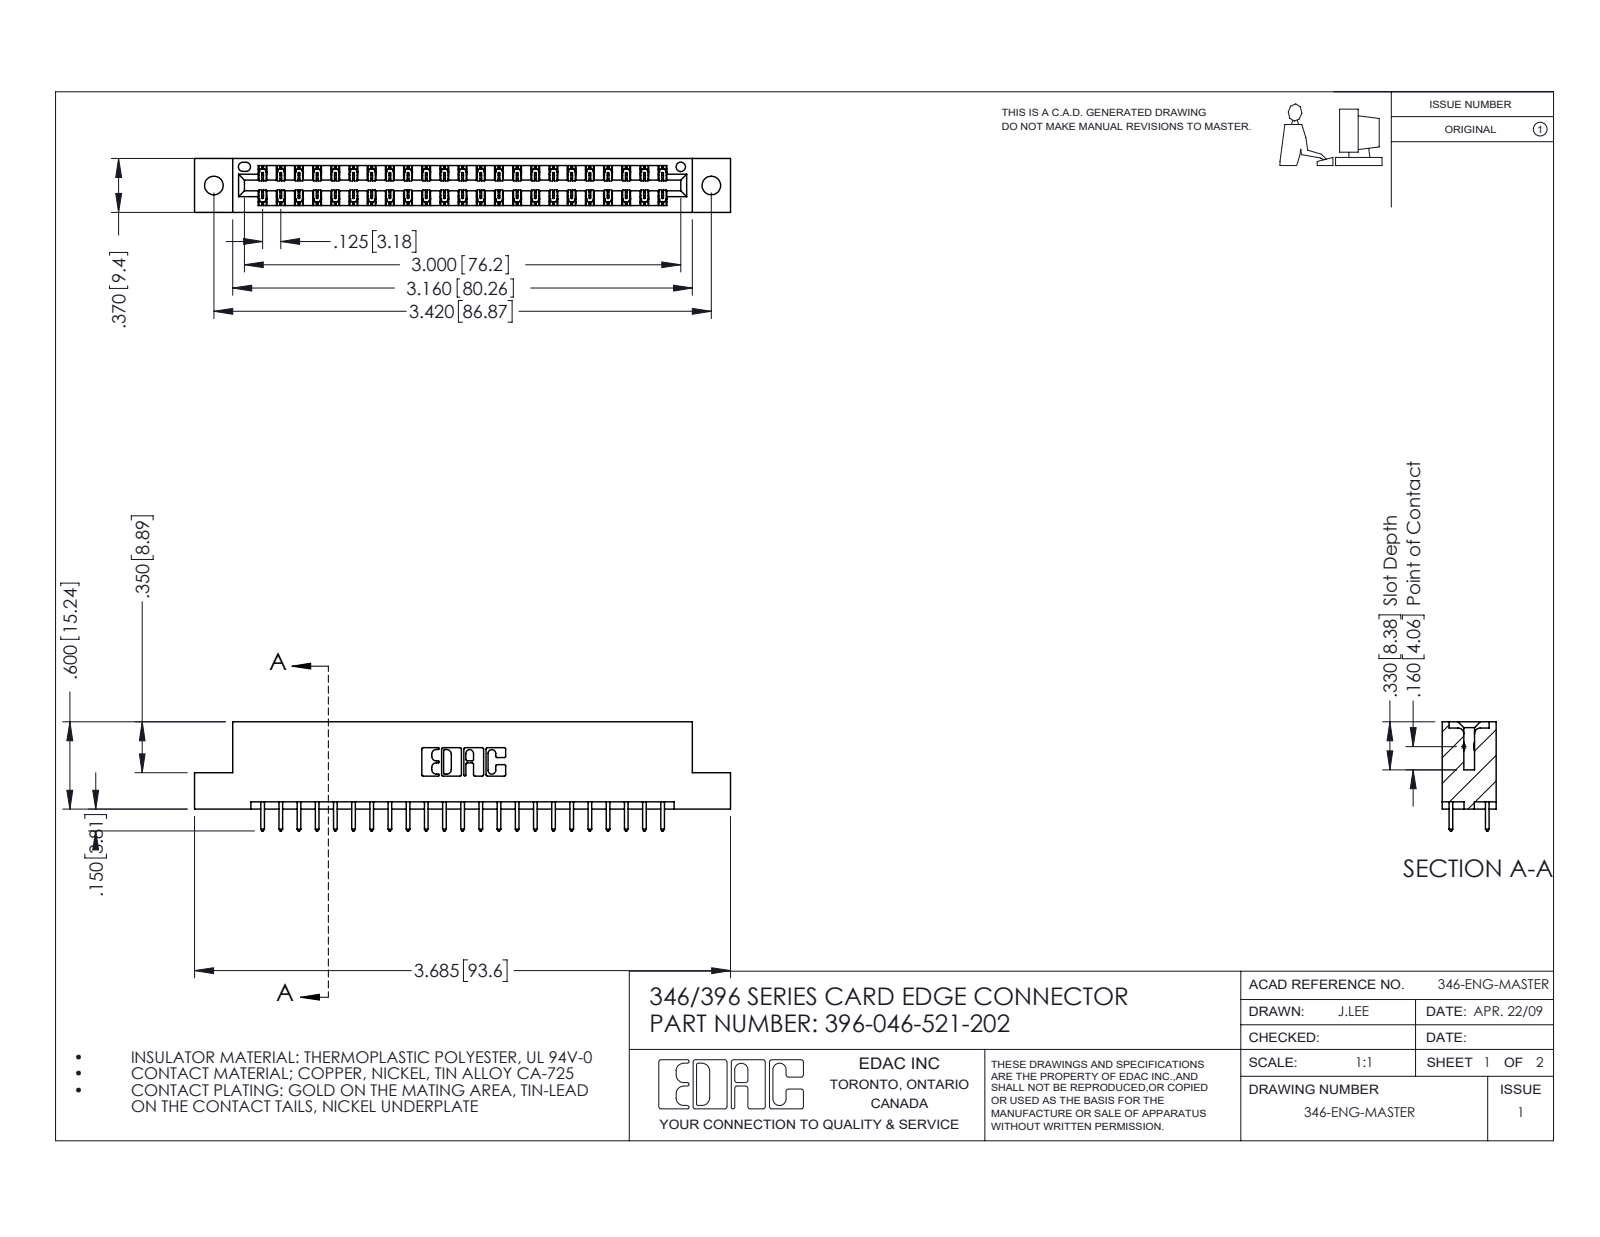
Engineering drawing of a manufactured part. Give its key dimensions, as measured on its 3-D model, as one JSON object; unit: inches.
{"part_name": "396-046-521-202; 345-292-001_345-293-121; 346 Part_Flush Mounting Lugs - 0.128 Dia", "step_written_by": "SolidWorks 2016 (CONFIG_CONTROL_DESIGN)", "units": "inches", "bodies": {"solids": 47, "faces": 2514, "planar": 1686, "cylindrical": 828, "other": 0}, "overall_size": [3.685, 0.75, 0.37], "volume_in3": 0.545, "surface_area_in2": 17.94, "round_holes": [[0.128, 2], [0.064, 1]], "partial_cylinders_radius": [[0.006, 69], [0.01, 46], [0.01, 22], [0.007, 6], [0.031, 6], [0.026, 3], [0.014, 2], [0.022, 2]], "face_to_face_distances": [0.048, 0.322, 0.25, 0.37, 0.072, 0.298, 0.025, 0.275, 0.148, 0.222], "hole_center_spacings": [0.246, 3.212, 3.42]}
